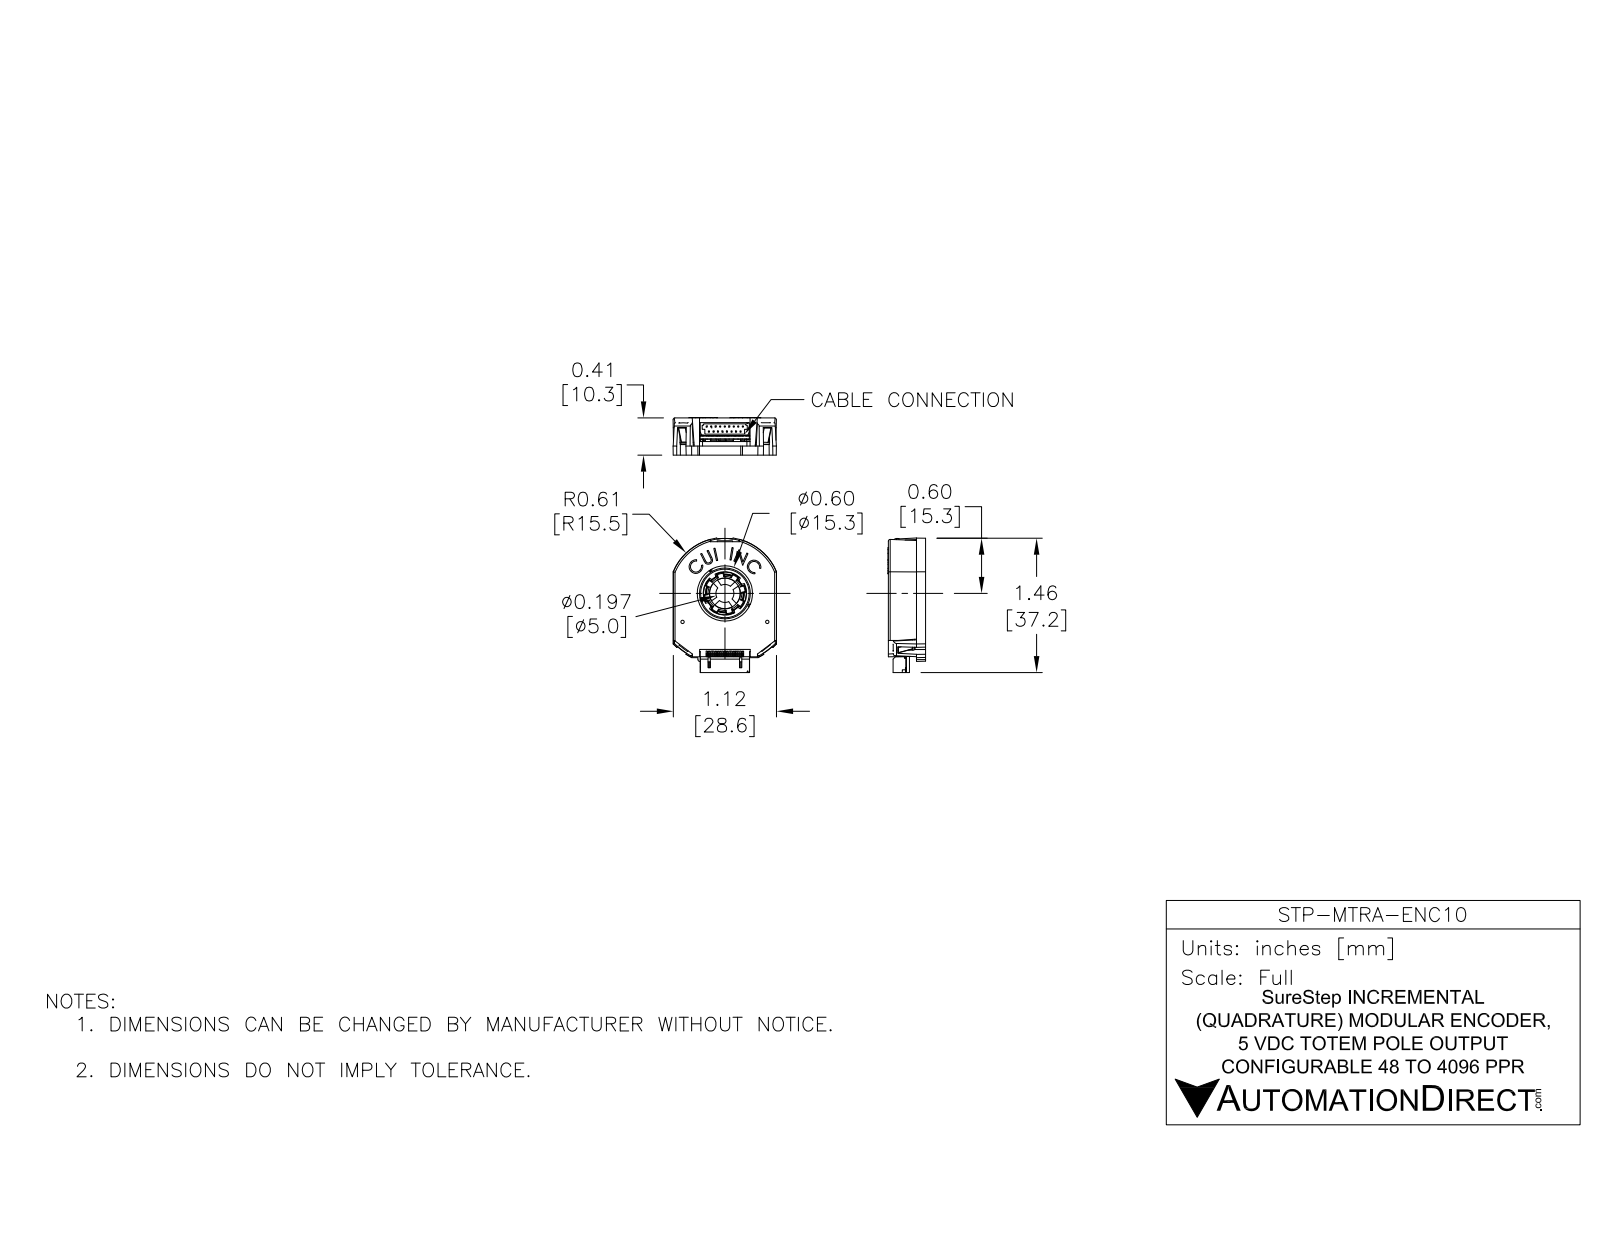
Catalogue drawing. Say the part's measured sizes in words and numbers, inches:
The part is named "STP-MTRA-ENC10". Its 3-D file was written by "SolidWorks 2017 (AUTOMOTIVE_DESIGN)". It is 7 solids with 1217 faces: 710 planar, 278 cylindrical and 229 other. Overall it measures 1.467 by 1.126 by 0.409 inches. Its volume is 0.298 cubic inches and its surface area 13.44 square inches. Round holes: 4 of diameter 0.031, 4 of diameter 0.037, 4 of diameter 0.079, 2 of diameter 0.067, 2 of diameter 0.091, 2 of diameter 0.116, 2 of diameter 0.161, 2 of diameter 0.177, 1 of diameter 0.472, 1 of diameter 0.496, 1 of diameter 0.56, 1 of diameter 0.602. Round bosses or shafts: 4 of diameter 0.059, 1 of diameter 0.465, 1 of diameter 0.413. Partial cylindrical surfaces (rounded edges, fillets, slot ends): 22 of radius 0.039, 6 of radius 0.02, 6 of radius 0.041, 6 of radius 0.079, 4 of radius 0.012, 4 of radius 0.016, 4 of radius 0.08, 3 of radius 0.004. The main face-to-face distances are 0.209, 0.175, 0.033, 0.406, 0.23, 0.197, 0.307, 0.098, 0.077, 0.11. The hole center spacings are 0.354, 0.5, 0.707, 0.81, 0.75, 0.078, 0.117, 0.172.
